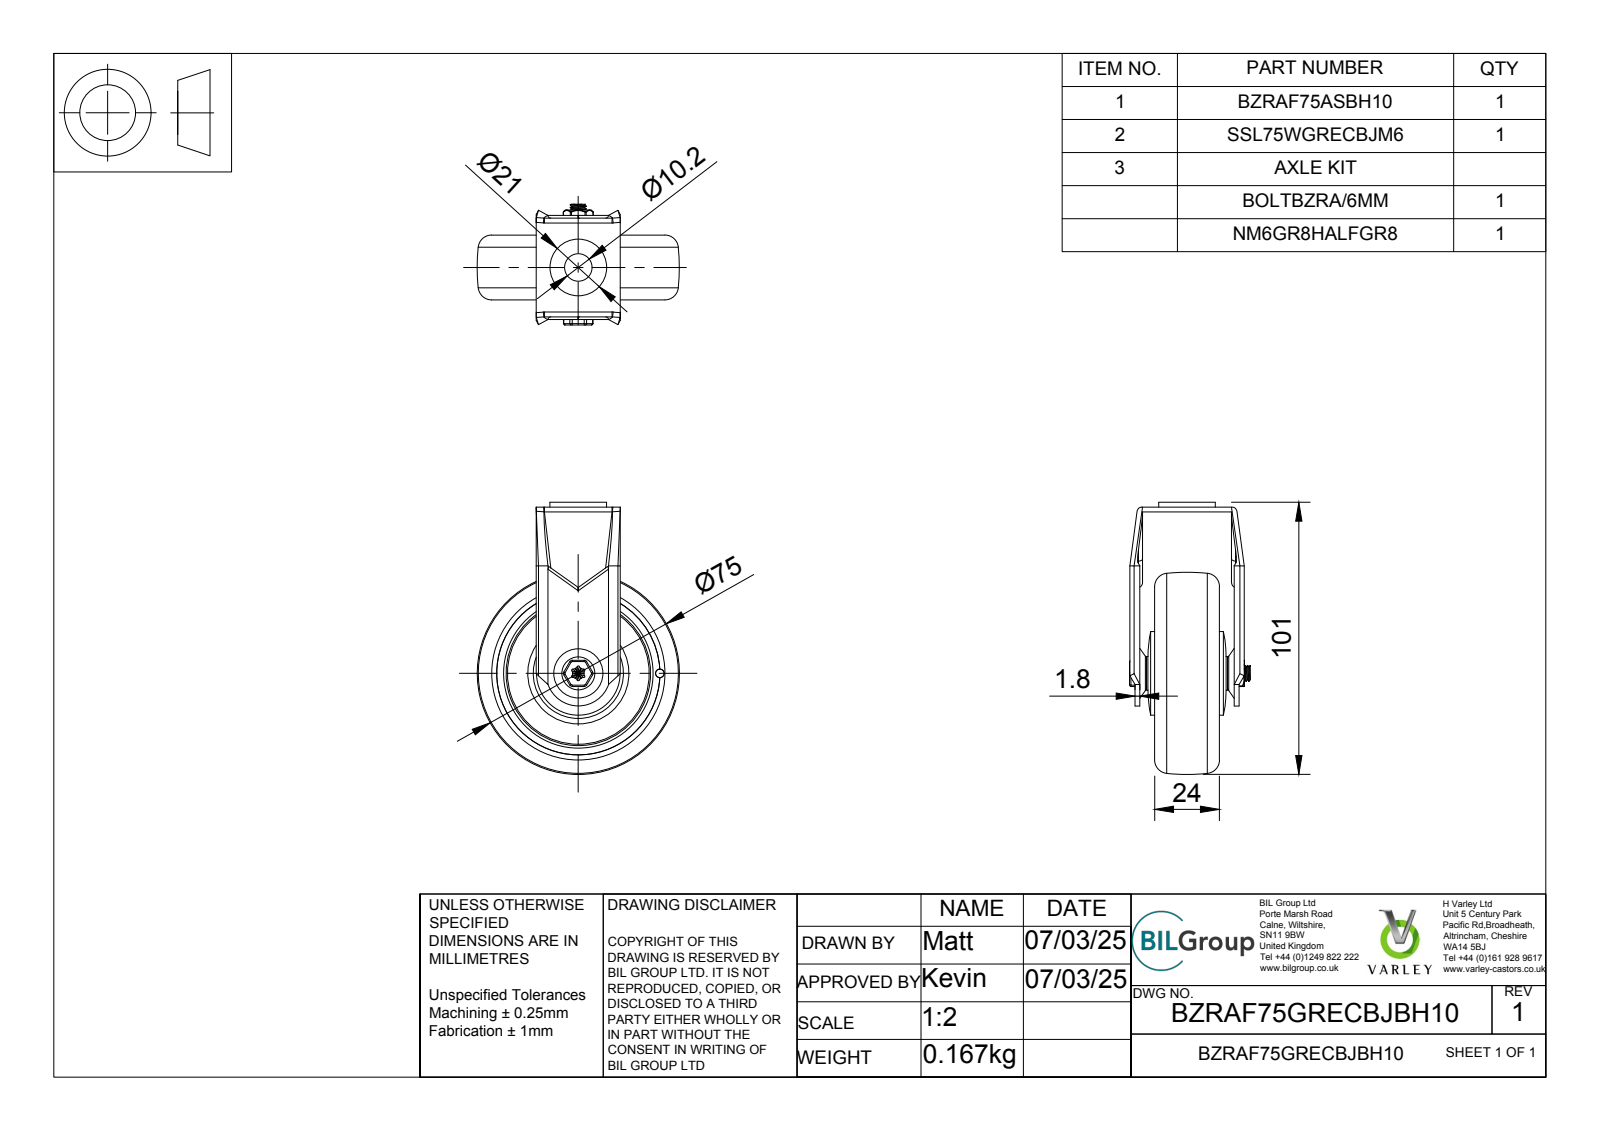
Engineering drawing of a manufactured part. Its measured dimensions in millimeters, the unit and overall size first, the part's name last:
Units: millimetres
Overall size (bounding box): 101 × 75 × 44.75
Round holes (diameter × count): ⌀3.2 ×1, ⌀6 ×1, ⌀6.2 ×1, ⌀8.2 ×1, ⌀10.2 ×1, ⌀11 ×1, ⌀11.5 ×1, ⌀18 ×1, ⌀19 ×1, ⌀20 ×1, ⌀22 ×1, ⌀28 ×1
Round bosses / shafts (diameter × count): ⌀37.5 ×1, ⌀21 ×1, ⌀18.5 ×1, ⌀12.5 ×1, ⌀12 ×1, ⌀10 ×1, ⌀8 ×1, ⌀5.88 ×1
Partial cylindrical surfaces — rounded edges, fillets, slot ends (radius × count): R1 ×26, R0.5 ×12, R1.5 ×8, R0.4 ×6, R0.99 ×4, R1.8 ×2, R2.12 ×1, R11.91 ×1
Main face-to-face distances: 1.8, 1, 35.8, 10.5, 13.5, 16, 5.5, 19, 29.5, 7.3
Hole centre spacings: 30.25
Volume: 80 978 mm³ · Surface area: 51 412 mm²
Bodies: 18 solids, 374 faces (110 planar, 138 cylindrical, 126 other)
Part name (STEP PRODUCT): BZRAF75GRECBJBH10 v3; SSL75WGRECBJM6 v1; ELECTRICALLY CONDUCTIVE RUBBER TYRE; ELECTRICALLY CONDUCTIVE RUBBER TYRE Geometry (+5 more)
STEP written by: Autodesk Translation Framework v13.20.0.188 (AP242_MANAGED_MODEL_BASED_3D_ENGINEERING_MIM_LF)
